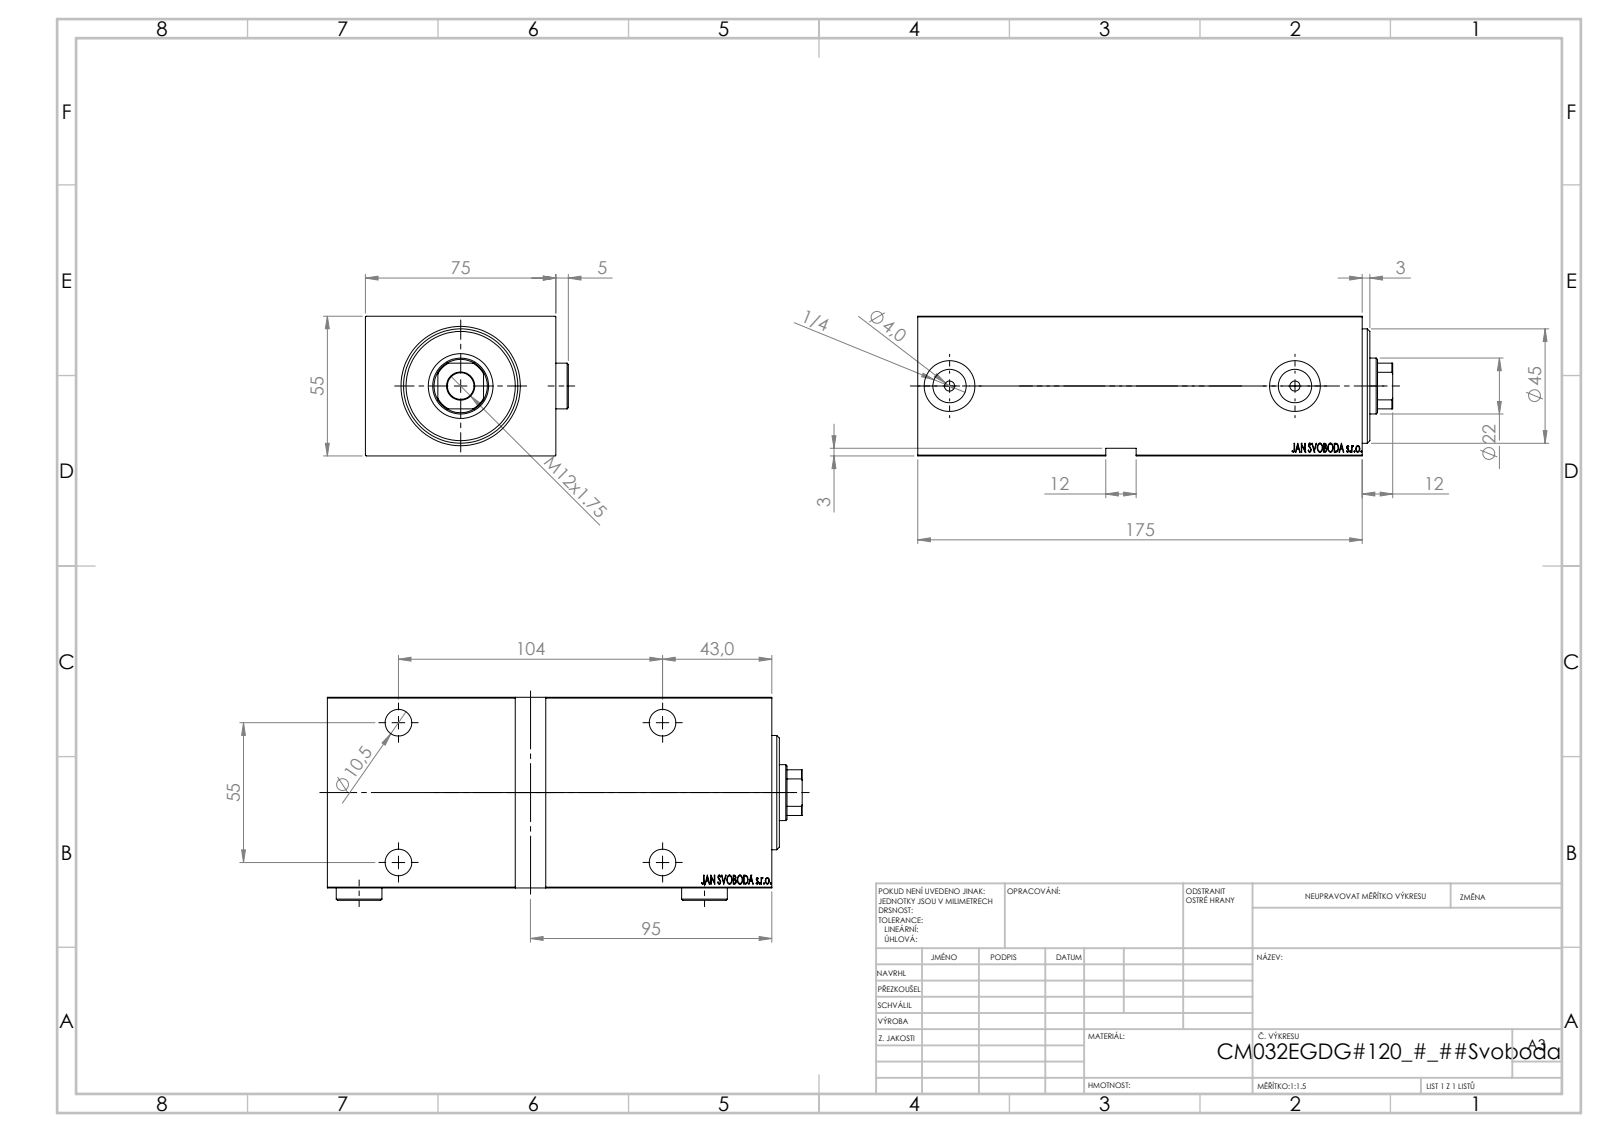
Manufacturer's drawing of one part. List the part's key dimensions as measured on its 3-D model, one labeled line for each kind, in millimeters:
Part name (STEP PRODUCT): V450CM_VC_B; V450CM_E_VCP; Zatka_OIL_PORT; V450CM_E_Body
STEP written by: SolidWorks 2019 (CONFIG_CONTROL_DESIGN)
Units: millimetres
Bodies: 5 solids, 909 faces (445 planar, 66 cylindrical, 398 other)
Overall size (bounding box): 187 × 79.9 × 55
Volume: 644 727 mm³ · Surface area: 104 303 mm²
Round holes (diameter × count): ⌀10.5 ×5, ⌀16.5 ×4, ⌀4 ×2, ⌀13.16 ×2, ⌀20 ×2, ⌀22 ×1, ⌀25.5 ×1, ⌀32 ×1, ⌀45 ×1
Round bosses / shafts (diameter × count): ⌀18 ×2, ⌀34 ×1
Partial cylindrical surfaces — rounded edges, fillets, slot ends (radius × count): R10.5 ×1
Main face-to-face distances: 55, 75, 175, 3, 5, 10, 165, 170, 160, 74.9
Hole centre spacings: 55, 104, 117.65, 136
